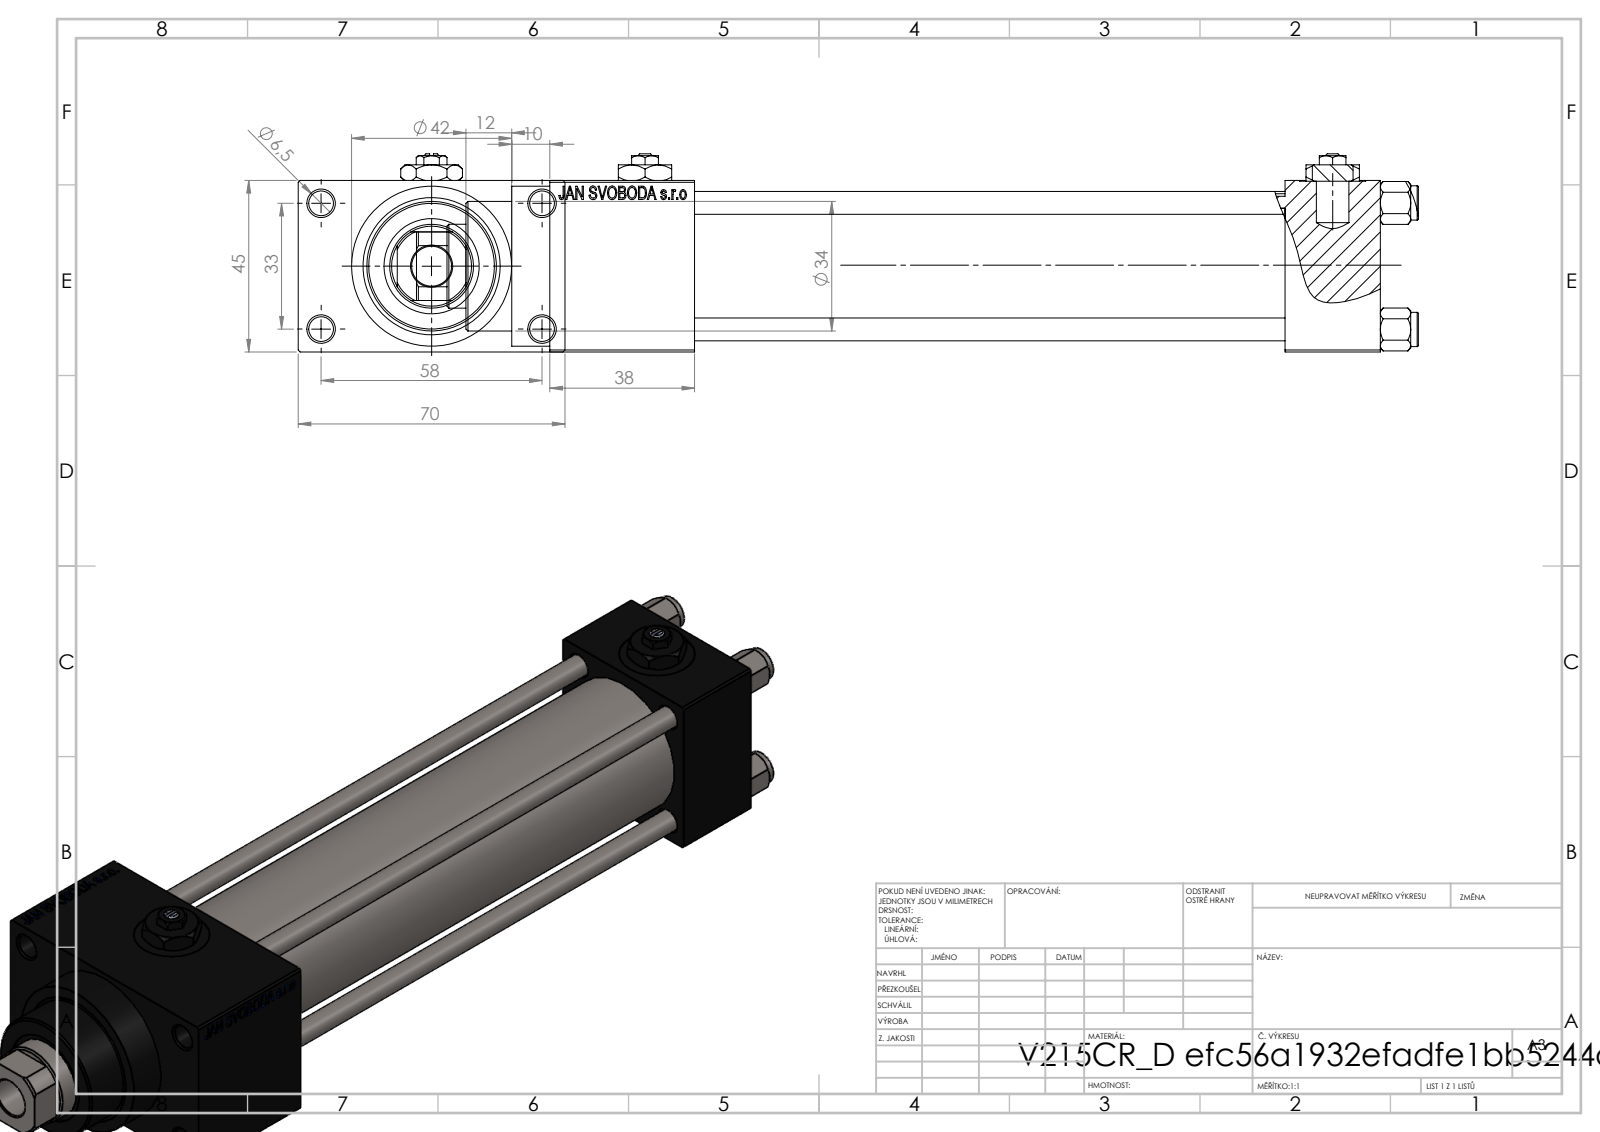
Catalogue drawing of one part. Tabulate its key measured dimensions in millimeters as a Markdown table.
| quantity | value |
| --- | --- |
| part name | NUT_M5_D; V215CR_D_TYCINKA; V215_VC_A; Zatka_pro_OIL_PORT (+2 more) |
| STEP written by | SolidWorks 2019 (CONFIG_CONTROL_DESIGN) |
| units | millimeters |
| bodies | 13 solids, 1203 faces (542 planar, 99 cylindrical, 562 other) |
| overall size | 263 × 70 × 52 |
| volume | 328 050 mm³ |
| surface area | 119 888 mm² |
| round holes (diameter × count) | 6 × 4, 6.5 × 4, 13.16 × 4, 20 × 4, 7 × 3, 10.5 × 1, 22 × 1, 24 × 1, 25 × 1, 32 × 1, 33 × 1 |
| round bosses / shafts (diameter × count) | 9 × 4, 42 × 1, 38 × 1, 34 × 1 |
| partial cylindrical surfaces (radius × count) | 10.5 × 1 |
| main face-to-face distances | 45, 25, 12.5, 155, 180, 57.5, 193, 38, 218, 70 |
| hole center spacings | 12.4, 23.48, 33.2, 33.37, 35.35, 45.6, 56.35, 33 |
